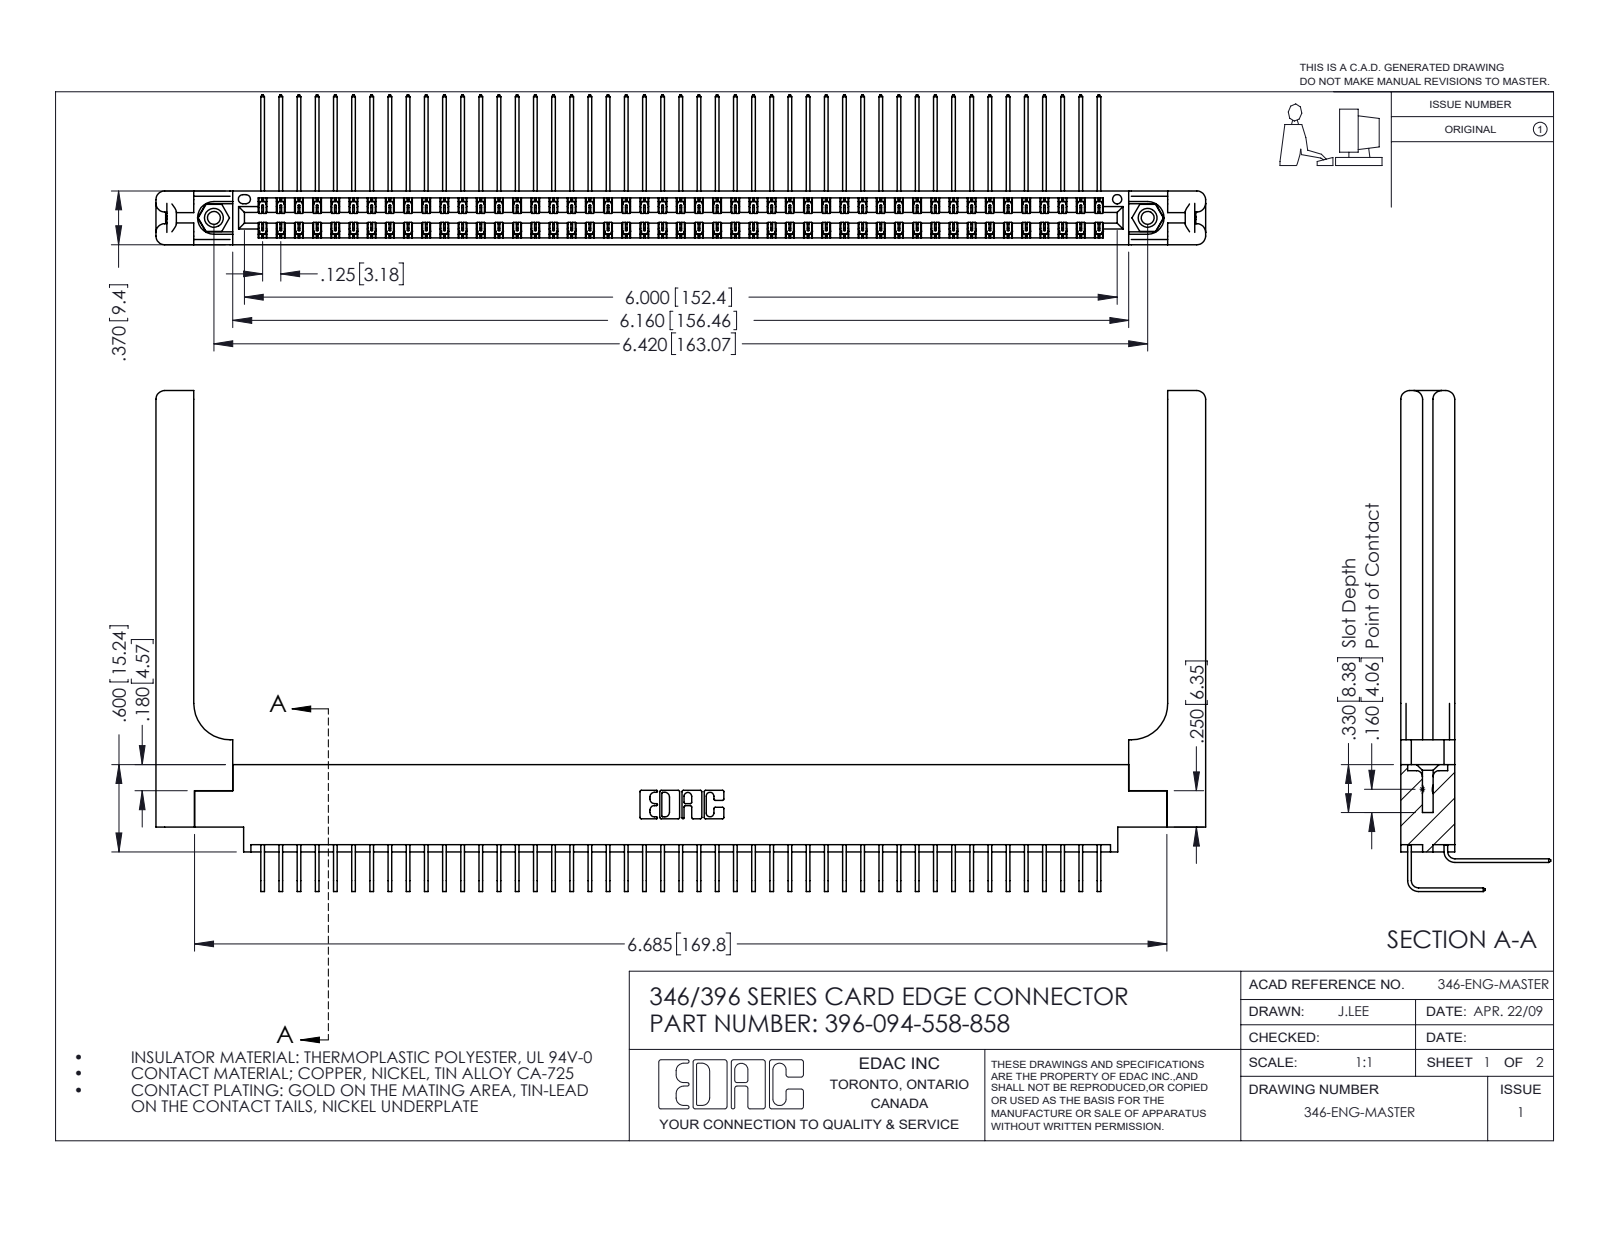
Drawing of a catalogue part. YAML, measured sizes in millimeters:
part_name: "396-094-558-858; 345-292-001_558 559 Tail - 1; 345-250-001_345-250-001-102; 345-292-001_558 Tail - 2 (+2 more)"
step_written_by: "SolidWorks 2016 (CONFIG_CONTROL_DESIGN)"
units: millimeters
bodies: {solids: 99, faces: 5458, planar: 3706, cylindrical: 1692, other: 60}
overall_size: [183.3, 87.5, 26.2]
volume: 25790
surface_area: 32990
round_holes:
  - {diameter: 2.3, count: 2}
  - {diameter: 3.2, count: 2}
  - {diameter: 4, count: 2}
  - {diameter: 1.6, count: 1}
round_bosses_or_shafts:
  - {diameter: 3.9, count: 2}
partial_cylinders:
  - {radius: 0.2, count: 141}
  - {radius: 0.3, count: 22}
  - {radius: 1.5, count: 16}
  - {radius: 0.2, count: 6}
  - {radius: 0.8, count: 6}
  - {radius: 0.7, count: 3}
  - {radius: 0.4, count: 2}
  - {radius: 0.6, count: 2}
face_to_face_distances: [8.2, 1.2, 9.4, 1.8, 0.6, 7.6, 3.8, 3.8, 6.4, 7]
hole_center_spacings: [6.2, 157.8, 163.1]
